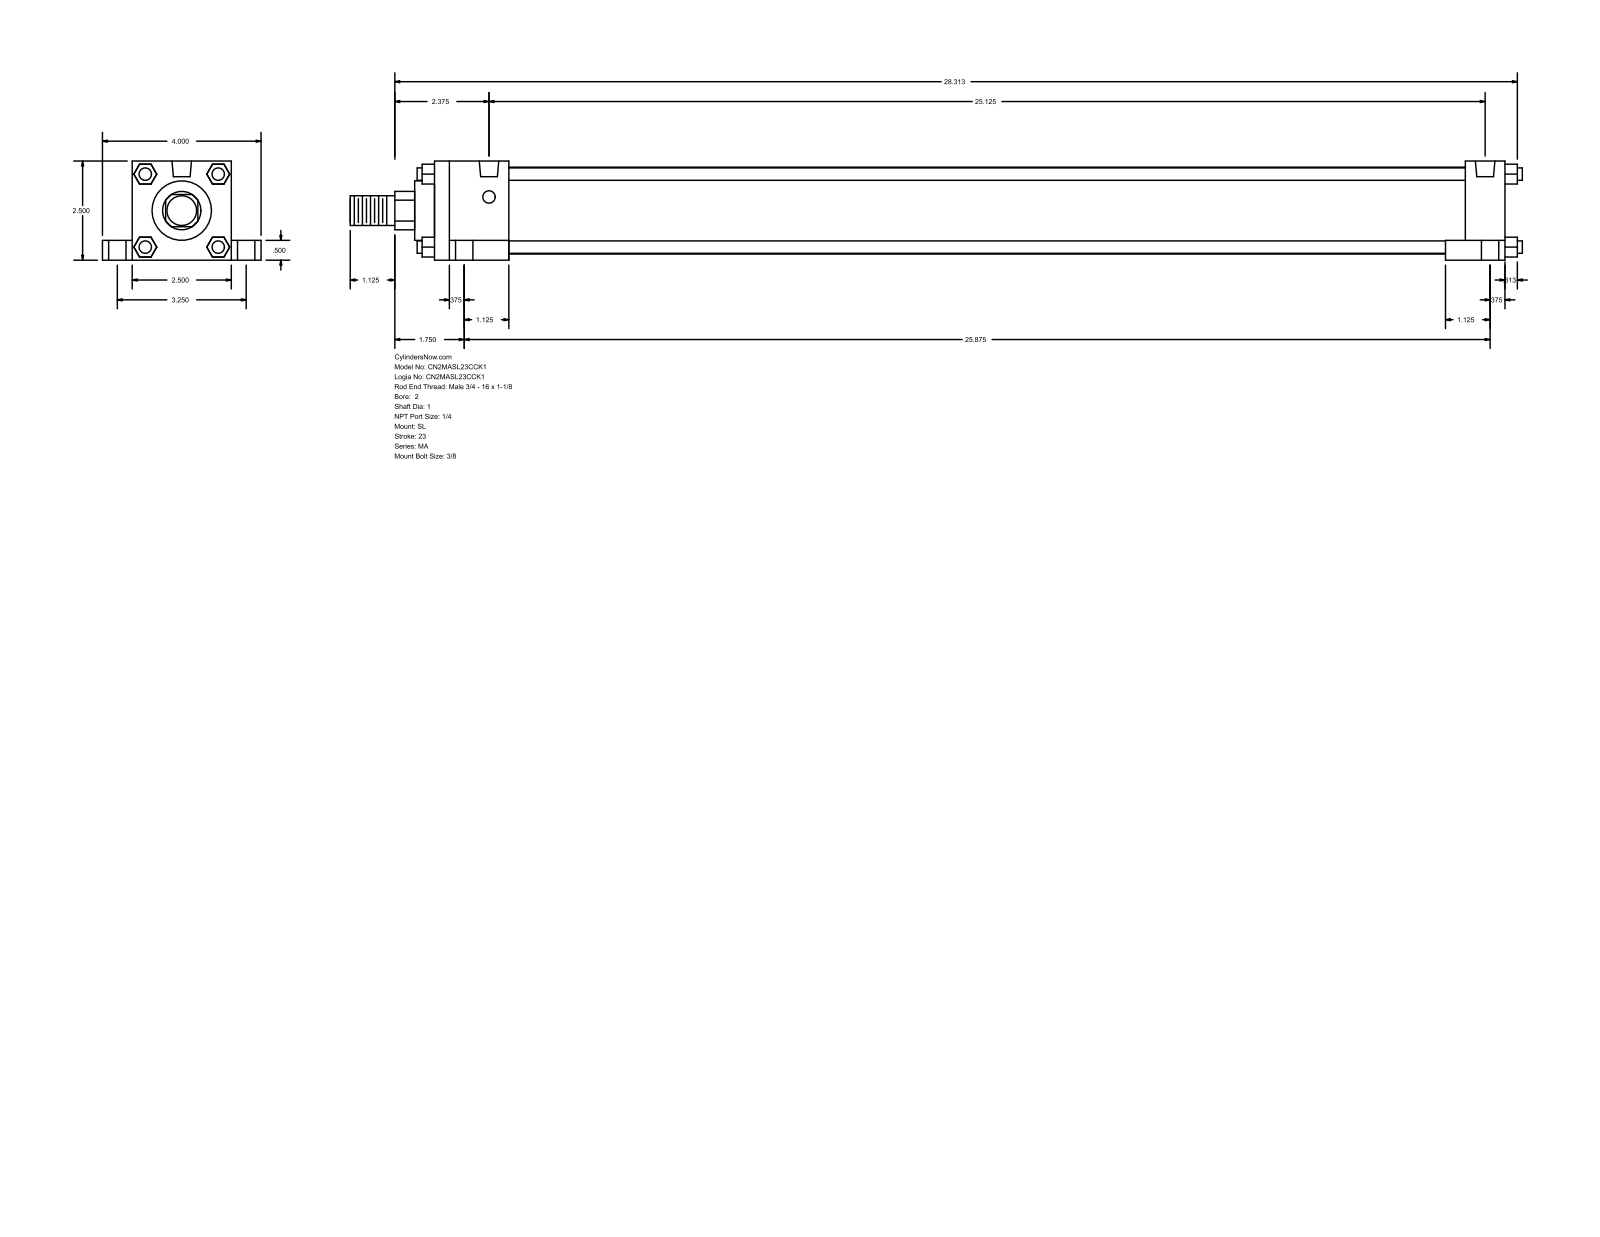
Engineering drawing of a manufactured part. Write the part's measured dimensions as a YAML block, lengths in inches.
part_name: "MA_SL__0200_1"
step_written_by: "GSSL Pune (CONFIG_CONTROL_DESIGN)"
units: inches
bodies: {solids: 0, faces: 148, planar: 112, cylindrical: 36, other: 0}
overall_size: [29.563, 4, 2.5]
round_holes:
  - {diameter: 0.313, count: 4}
  - {diameter: 0.437, count: 4}
  - {diameter: 0.687, count: 4}
  - {diameter: 0.492, count: 2}
round_bosses_or_shafts:
  - {diameter: 0.313, count: 4}
  - {diameter: 2.19, count: 1}
  - {diameter: 1.5, count: 1}
  - {diameter: 1, count: 1}
  - {diameter: 0.75, count: 1}
partial_cylinders:
  - {radius: 0.484, count: 1}
face_to_face_distances: [2.5, 0.5, 27, 0.75, 3.25, 1, 2, 1.875, 25.125, 26]
hole_center_spacings: [1.63, 1.741, 3.25, 25.125, 25.302, 25.801, 25.875, 26.078]
